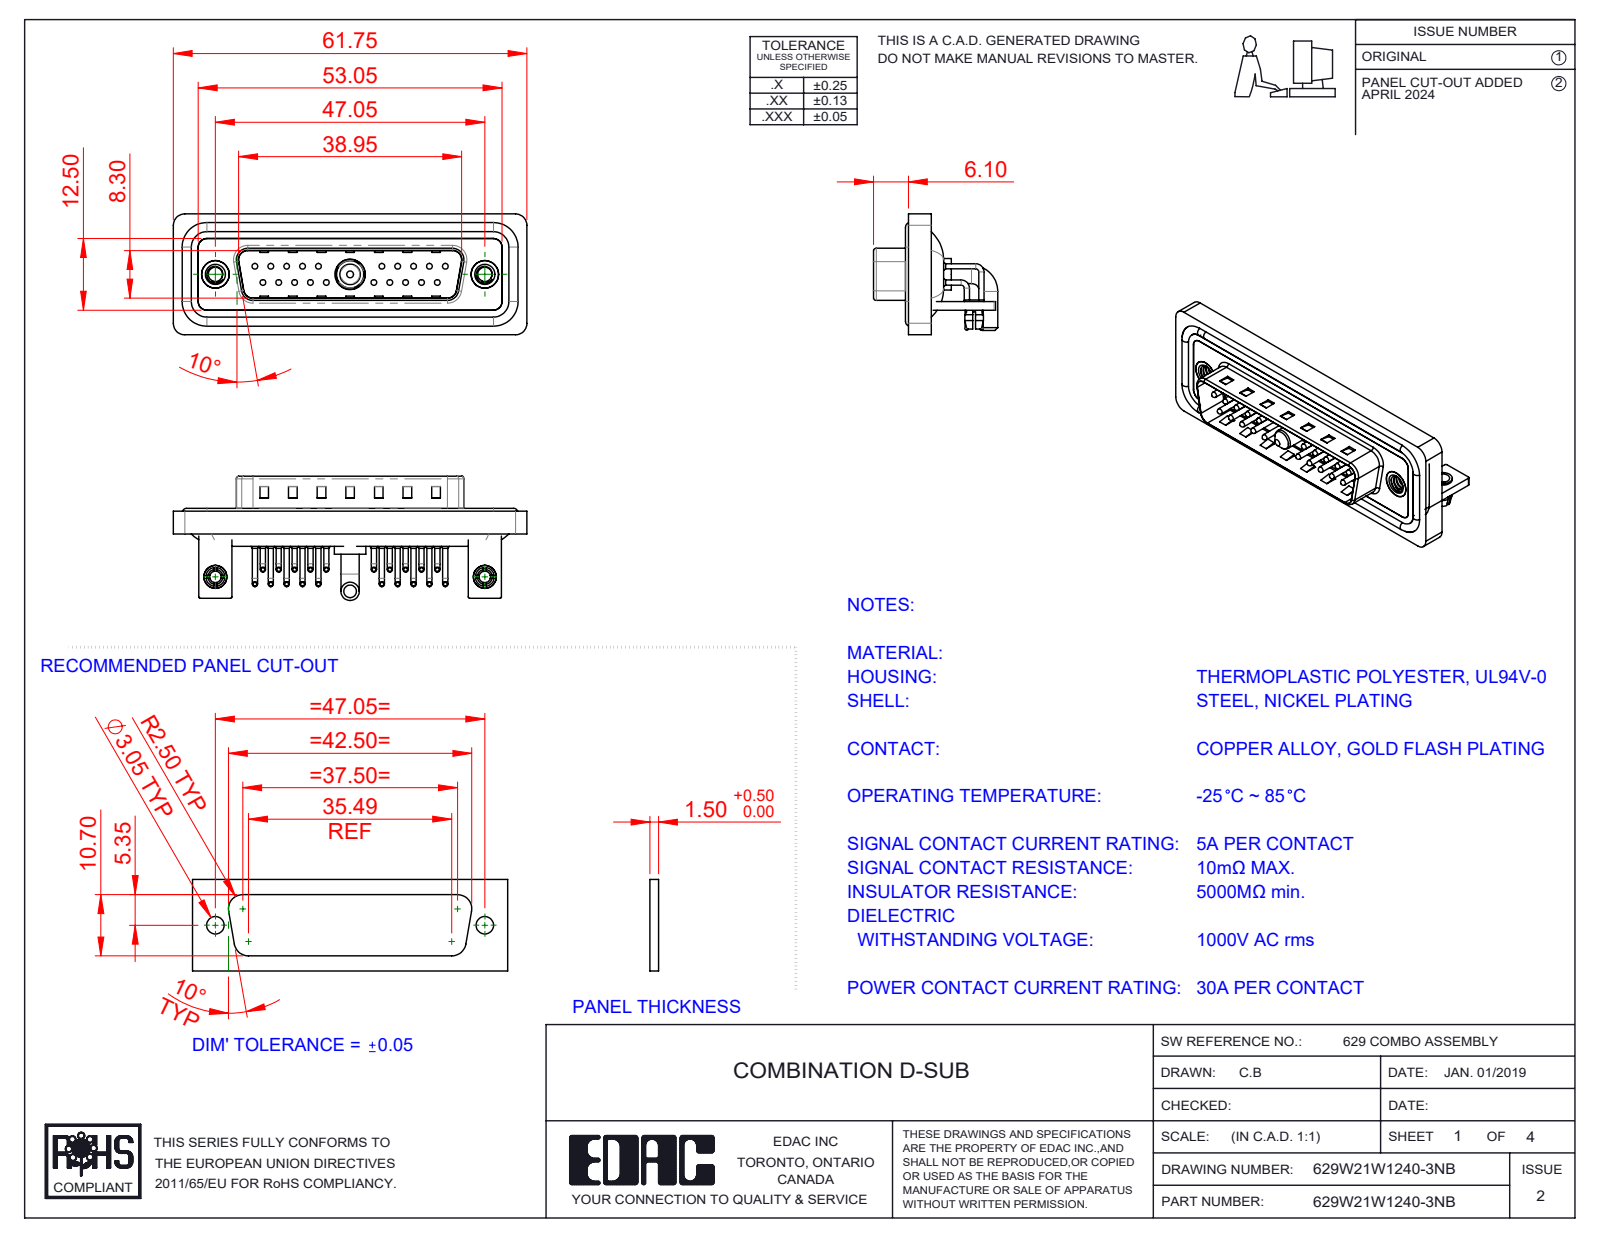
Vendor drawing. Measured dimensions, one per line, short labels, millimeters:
name: 629Combo Housing_21W1; 629Combo Contact Row 2; 629W21W1240-3NB; 629Combo Shell Rear_25 Contacts (+7 more)
written by: SolidWorks 2023 (CONFIG_CONTROL_DESIGN)
unit: mm
bodies: 33 solids, 2856 faces (1567 planar, 979 cylindrical, 310 other)
size: 61.75 × 21.7 × 21.1
volume: 7 754 mm³; area: 13 538 mm²
holes: 22× ⌀2, 20× ⌀0.75, 20× ⌀1.6, 4× ⌀2.5, 2× ⌀3.2, 2× ⌀4, 2× ⌀4.8, 2× ⌀5, 1× ⌀4.85, 1× ⌀5.3
bosses: 40× ⌀0.9, 20× ⌀1.5, 20× ⌀1, 20× ⌀0.65, 4× ⌀1.6, 2× ⌀4.9, 2× ⌀4, 2× ⌀3.4
rounds: 20× R1.01, 19× R2, 18× R1.5, 16× R0.25, 9× R0.5, 8× R1.6, 4× R0.6, 4× R0.65
face distances: 0.4, 0.8, 2.1, 2.9, 1.5, 1.1, 4.1, 1.6, 4.5, 3.7
hole spacings: 3.16, 2.77, 5.54, 8.31, 5.04, 19.39, 20.97, 22.16
